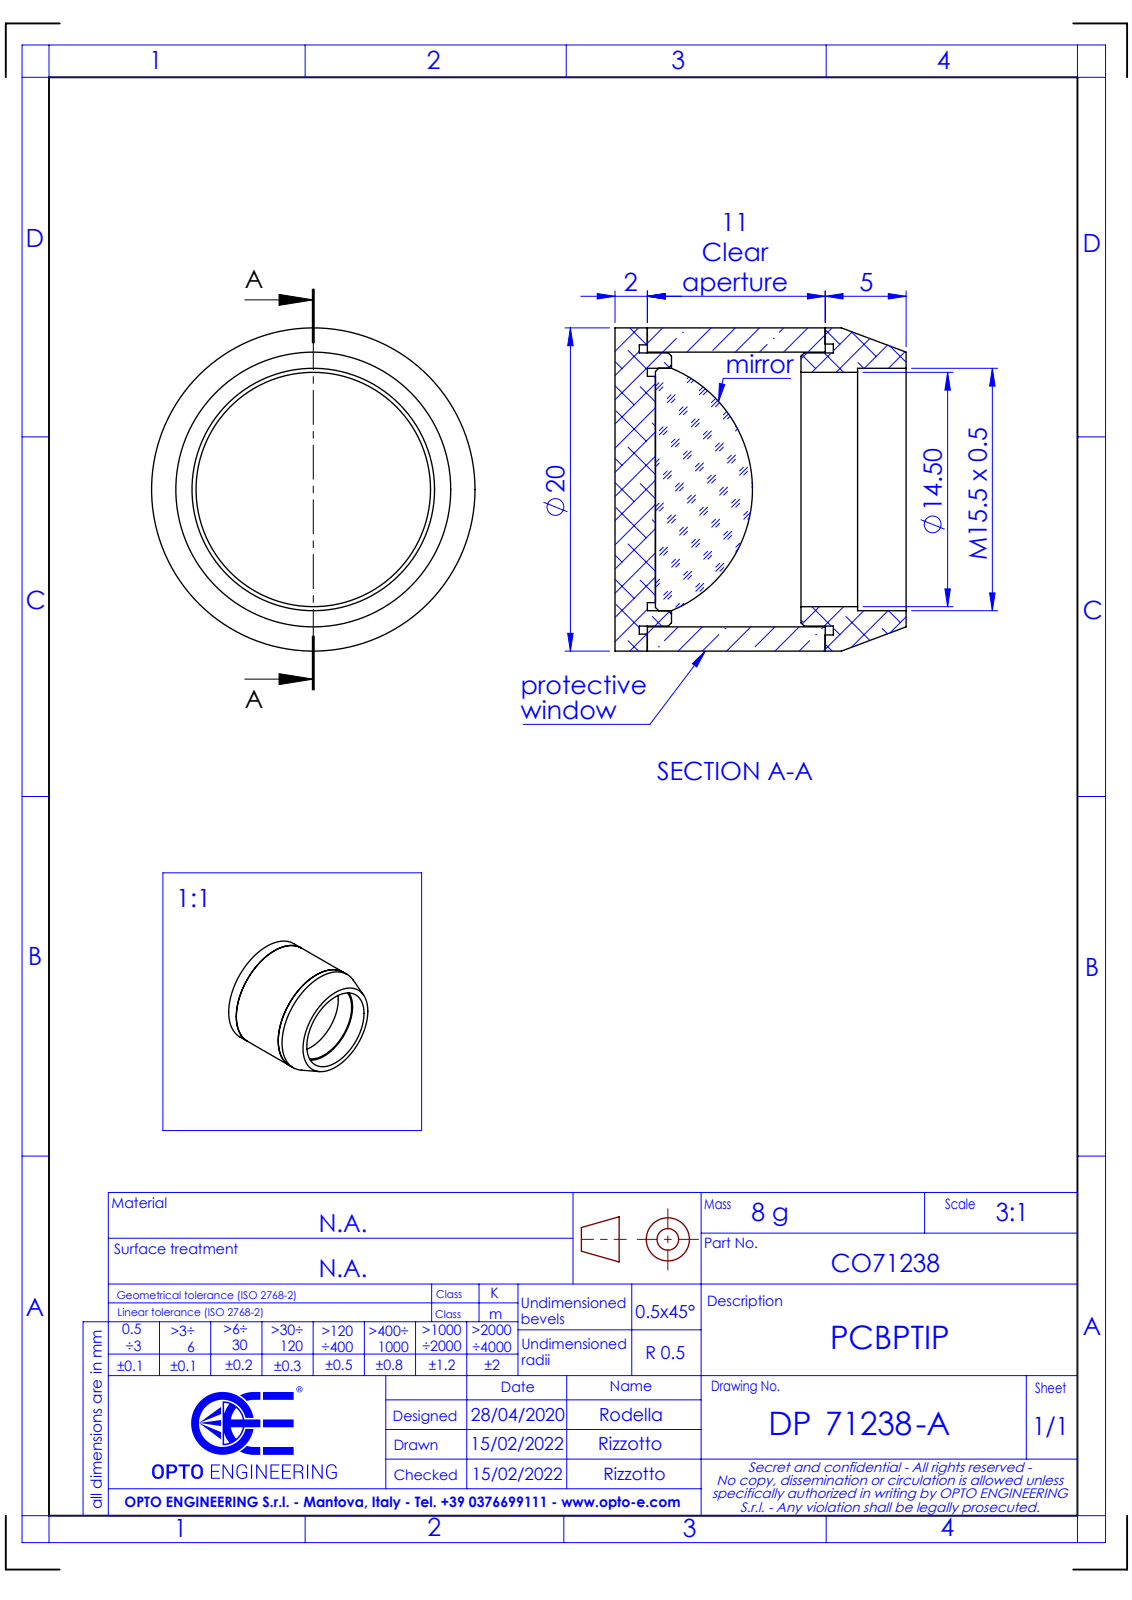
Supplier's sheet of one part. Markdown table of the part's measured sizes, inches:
| quantity | value |
| --- | --- |
| part name | DP71238-A_Punta con specchio__PCBP |
| STEP written by | SolidWorks 2021 (CONFIG_CONTROL_DESIGN) |
| units | inches |
| bodies | 0 solids, 17 faces (3 planar, 12 cylindrical, 2 other) |
| overall size | 0.787 × 0.787 × 0.709 |
| round holes (diameter × count) | 0.571 × 1, 0.591 × 1, 0.669 × 1 |
| round bosses / shafts (diameter × count) | 0.787 × 1 |
| main face-to-face distances | 0.709, 0.118, 0.591 |
